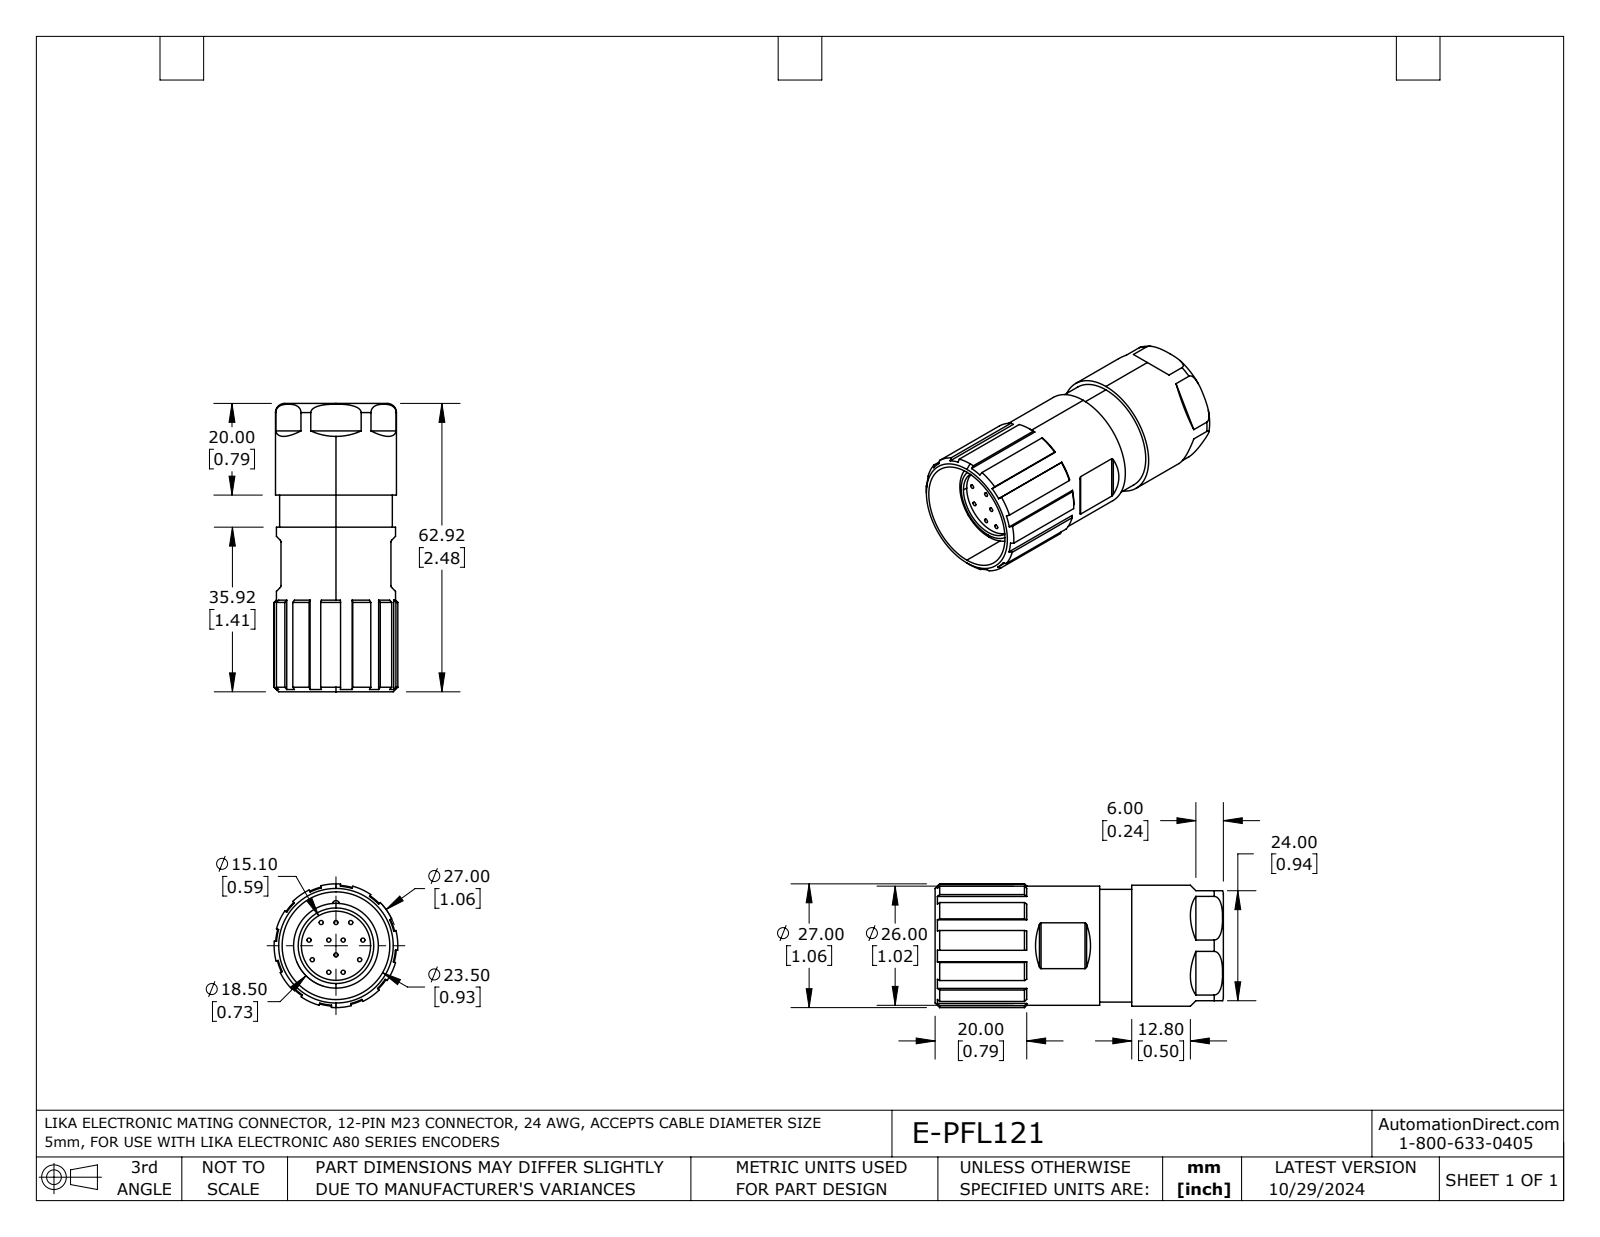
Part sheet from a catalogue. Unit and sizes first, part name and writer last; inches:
Units: inches
Overall size (bounding box): 2.477 × 1.063 × 1.063
Round holes (diameter × count): ⌀0.035 ×12, ⌀0.217 ×1, ⌀0.594 ×1, ⌀0.677 ×1, ⌀0.925 ×1
Round bosses / shafts (diameter × count): ⌀1.039 ×1, ⌀1.024 ×1, ⌀0.969 ×1, ⌀0.728 ×1
Partial cylindrical surfaces — rounded edges, fillets, slot ends (radius × count): R0.02 ×4, R0.03 ×1, R0.531 ×1
Main face-to-face distances: 0.945, 1.985, 0.335, 1.65, 2.182, 1.847, 0.197, 0.591, 1.394, 1.06
Hole centre spacings: 0.236, 0.079, 0.124, 0.127, 0.142, 0.162, 0.163, 0.164
Volume: 1.675 in³ · Surface area: 14.01 in²
Bodies: 1 solid, 146 faces (64 planar, 63 cylindrical, 19 other)
Part name (STEP PRODUCT): E-PFL121
STEP written by: SolidWorks 2021 (AUTOMOTIVE_DESIGN)
